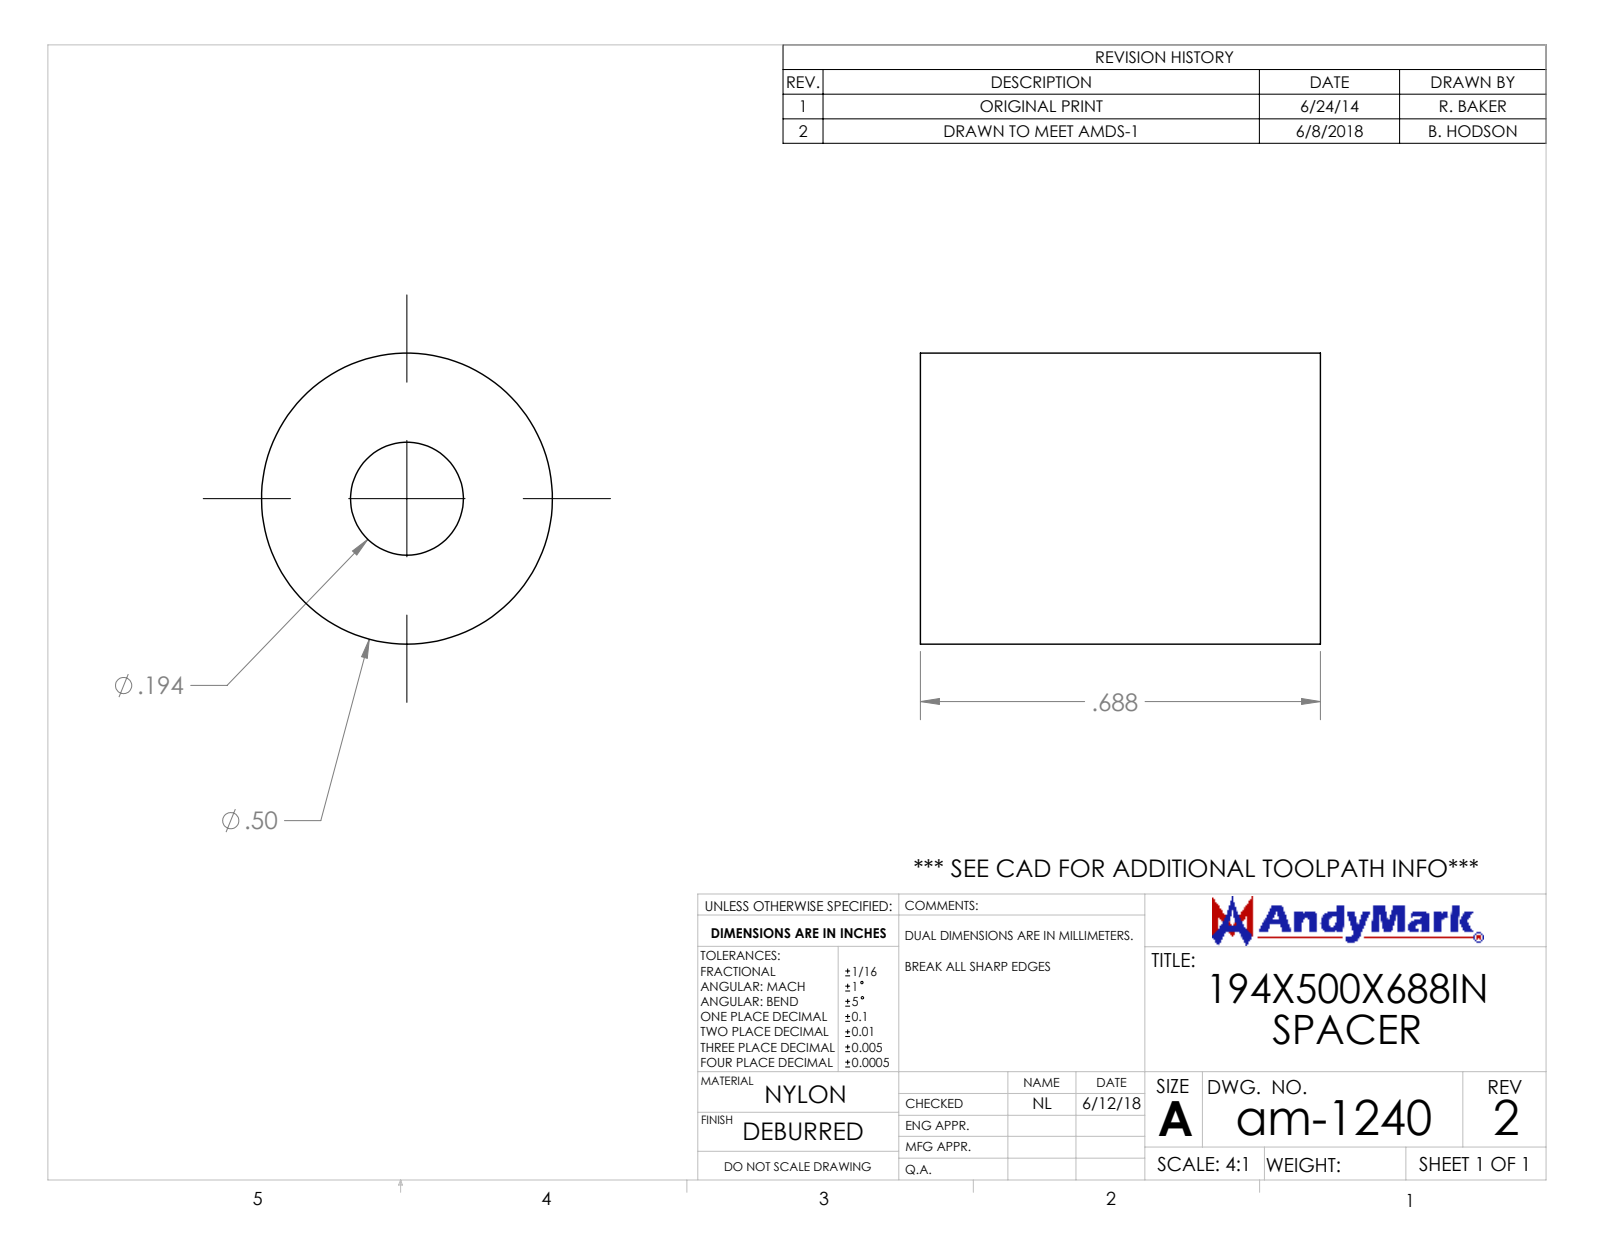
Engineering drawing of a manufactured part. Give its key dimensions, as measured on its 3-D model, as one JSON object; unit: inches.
{"part_name": "am-1240 11-16'''''''' Thick Nylon Spacer REV2", "step_written_by": "SolidWorks 2017 (AUTOMOTIVE_DESIGN)", "units": "inches", "bodies": {"solids": 1, "faces": 6, "planar": 2, "cylindrical": 4, "other": 0}, "overall_size": [0.687, 0.5, 0.5], "volume_in3": 0.115, "surface_area_in2": 1.833, "round_holes": [[0.194, 1]], "round_bosses_or_shafts": [[0.5, 1]], "face_to_face_distances": [0.687]}
